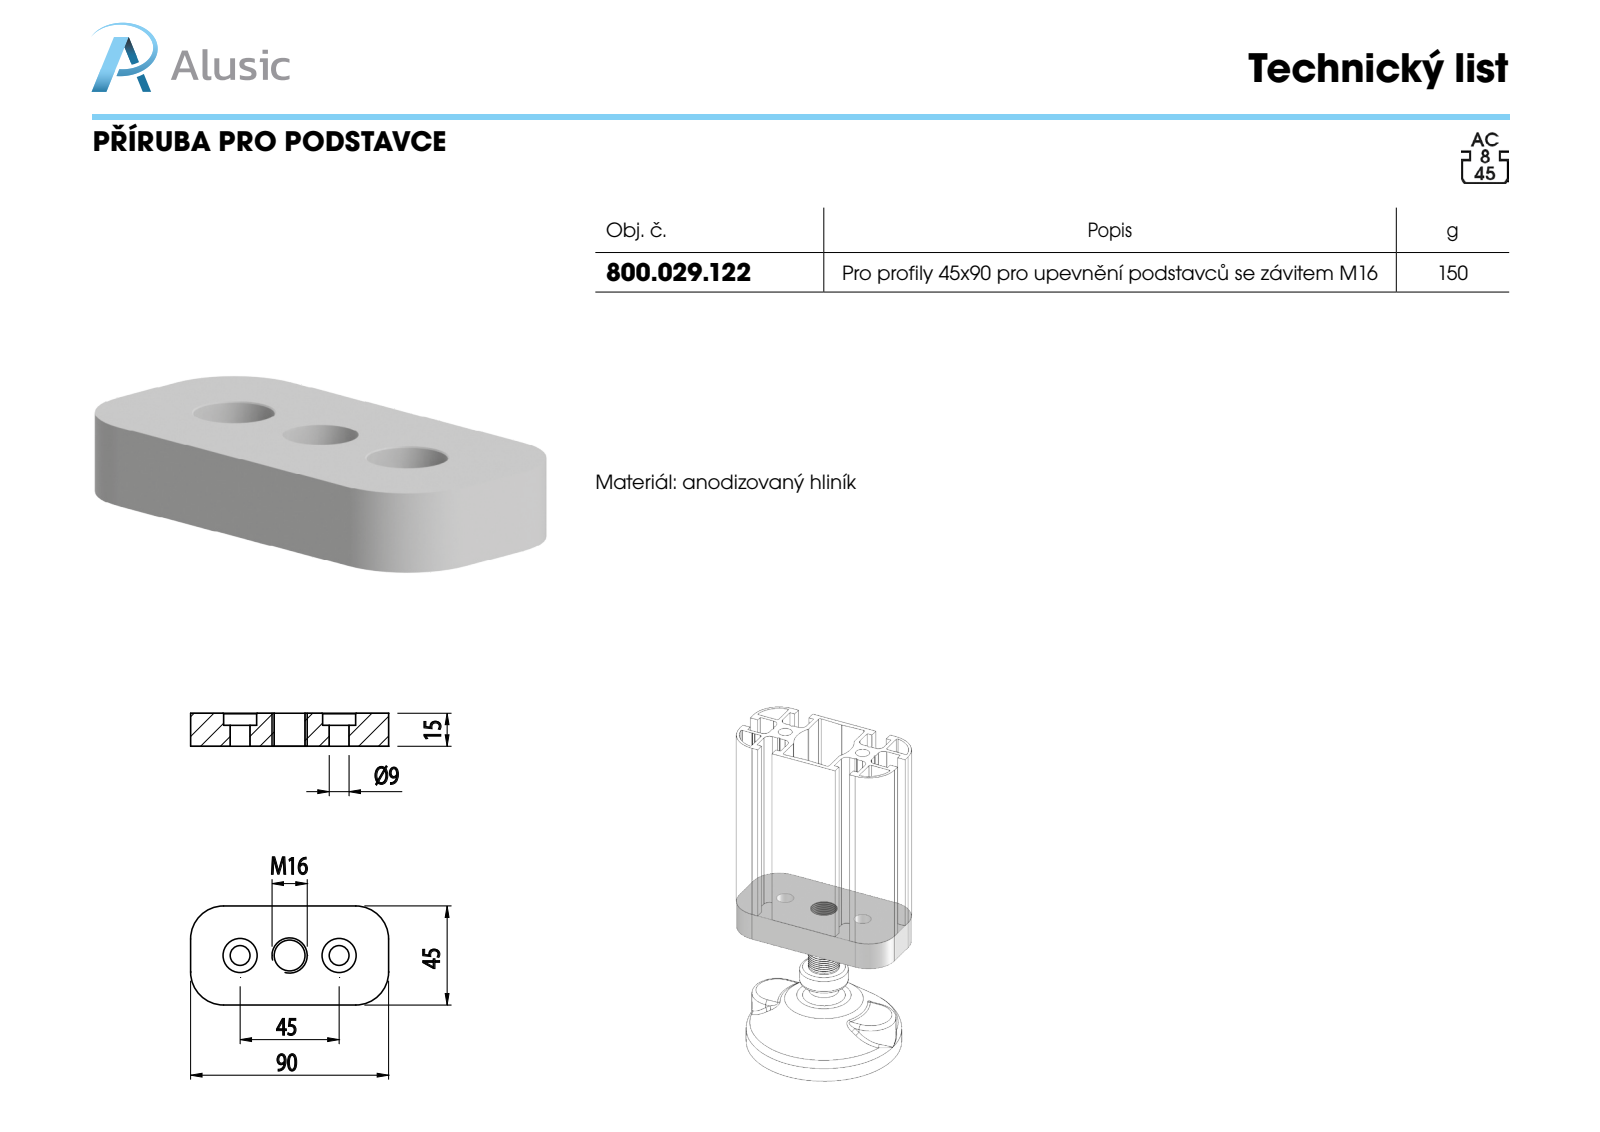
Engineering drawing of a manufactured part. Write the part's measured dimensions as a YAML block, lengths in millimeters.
part_name: "800.029.122"
step_written_by: "SolidWorks 2011 (CONFIG_CONTROL_DESIGN)"
units: millimeters
bodies: {solids: 1, faces: 26, planar: 8, cylindrical: 14, other: 4}
overall_size: [90, 45, 15]
volume: 52388
surface_area: 12517
round_holes:
  - {diameter: 9, count: 2}
  - {diameter: 15, count: 2}
  - {diameter: 14, count: 1}
partial_cylinders:
  - {radius: 15, count: 4}
face_to_face_distances: [15, 45, 9.5, 5.5, 90]
hole_center_spacings: [22.5, 45]
